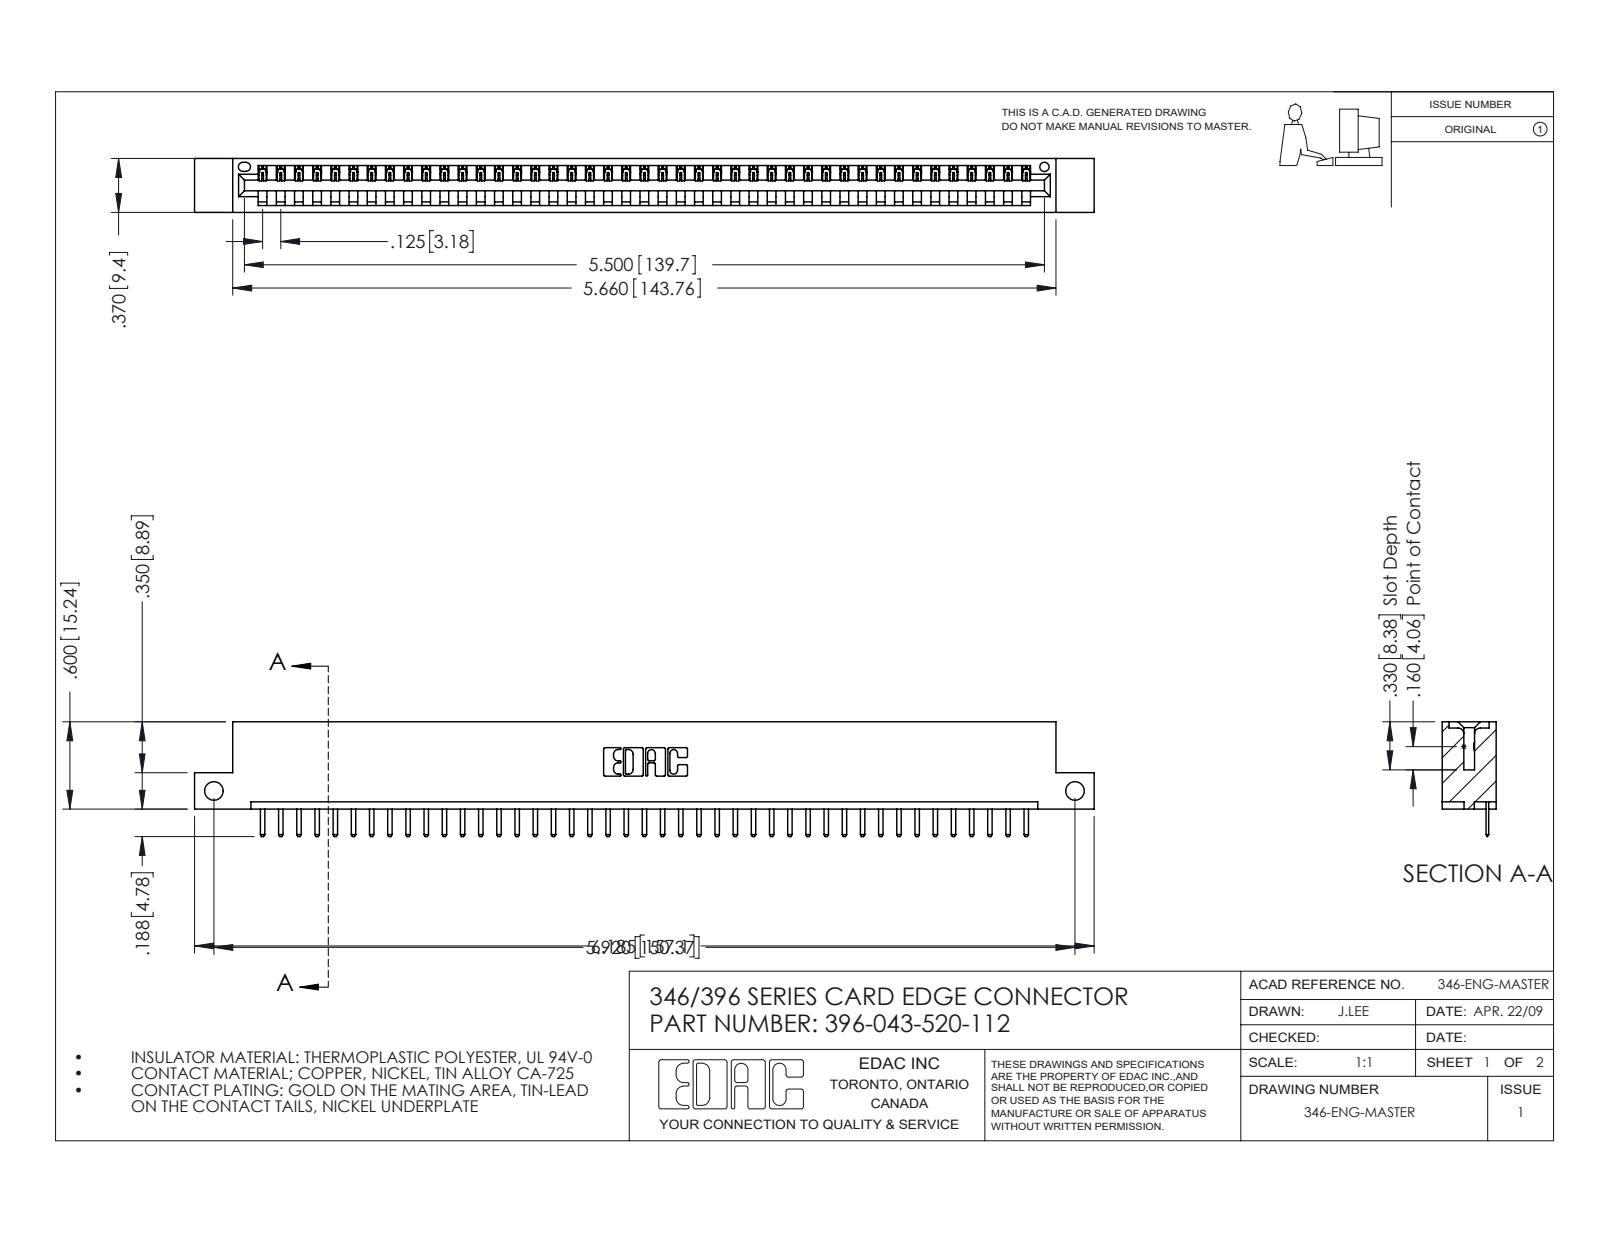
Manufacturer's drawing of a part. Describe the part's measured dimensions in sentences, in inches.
The part is named "345-292-001_345-293-120; 396-043-520-112; 346 Part_Flush Mounting Lugs - Side Mount". Its 3-D file was written by "SolidWorks 2016 (CONFIG_CONTROL_DESIGN)". It is 44 solids with 2788 faces: 1882 planar, 906 cylindrical and 0 other. Overall it measures 6.185 by 0.788 by 0.37 inches. Its volume is 0.905 cubic inches and its surface area 27.89 square inches. Round holes: 2 of diameter 0.128, 1 of diameter 0.064. Partial cylindrical surfaces (rounded edges, fillets, slot ends): 88 of radius 0.01, 86 of radius 0.006, 22 of radius 0.01, 6 of radius 0.007, 6 of radius 0.031, 3 of radius 0.026, 2 of radius 0.031, 2 of radius 0.04. The main face-to-face distances are 0.048, 0.322, 0.37, 0.25, 0.148, 0.222, 0.1, 0.174, 0.072, 0.298. The hole center spacings are 5.92.
